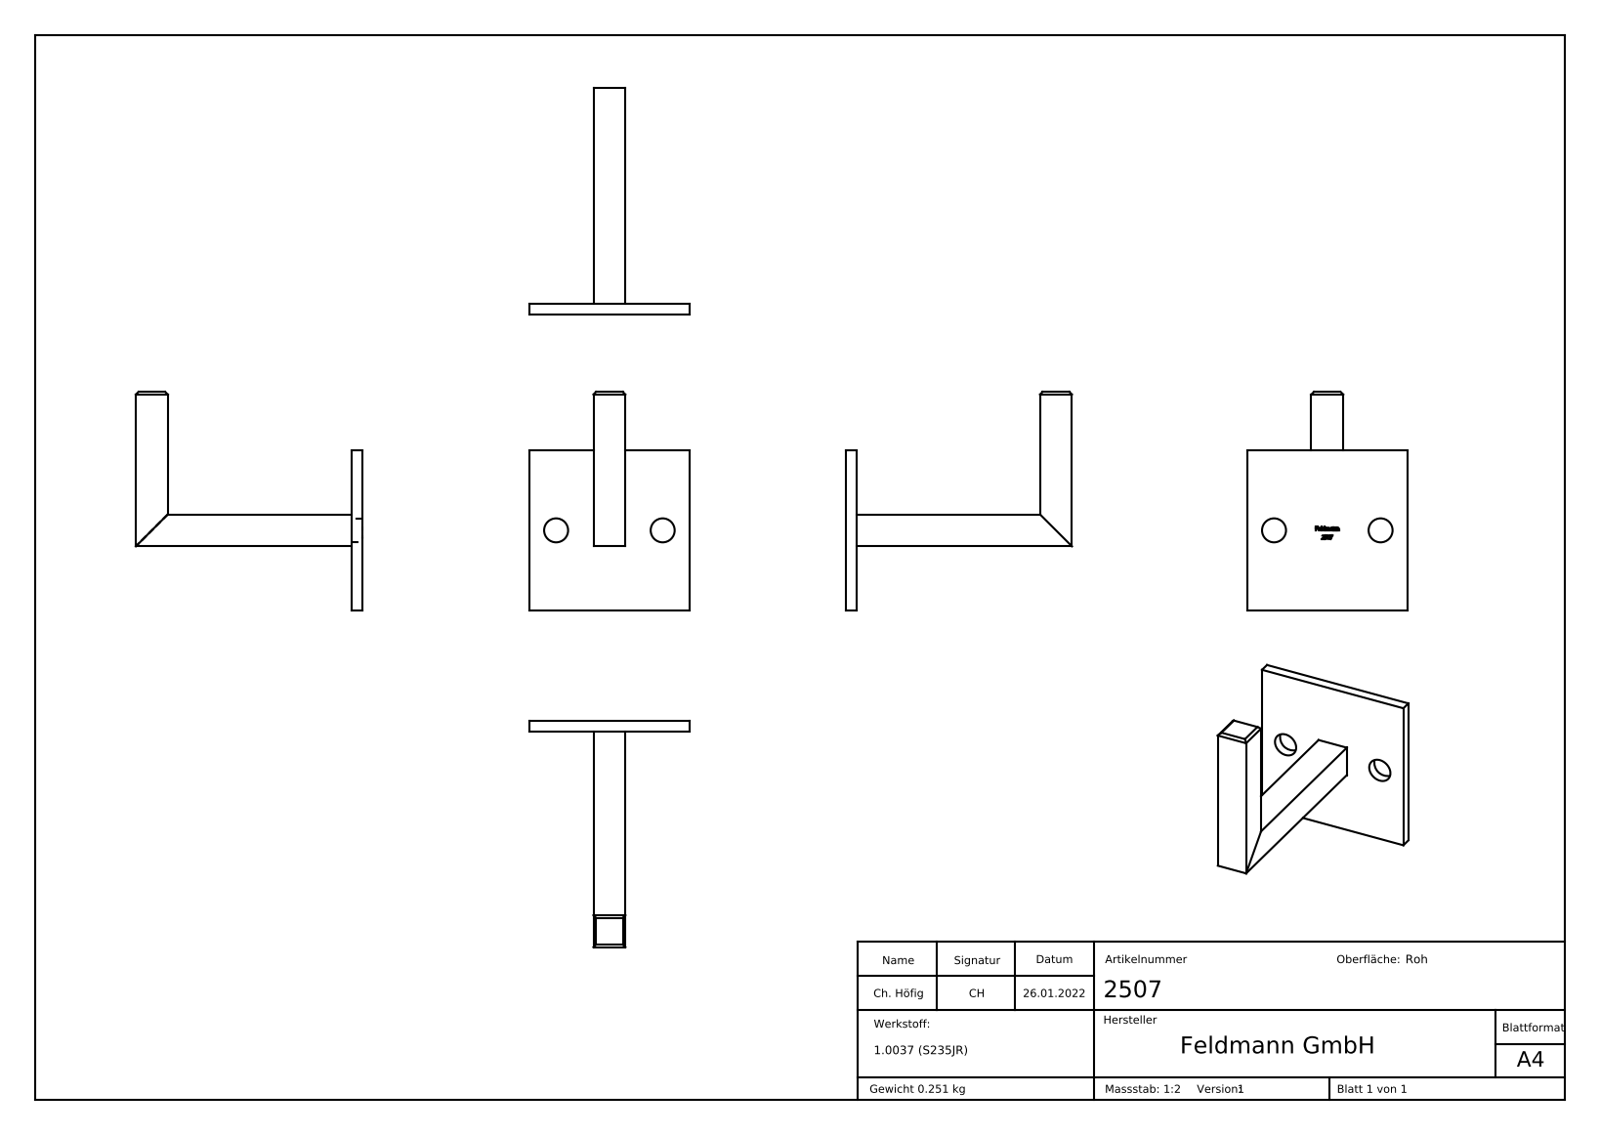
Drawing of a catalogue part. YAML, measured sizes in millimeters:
part_name: "2507"
step_written_by: "SolidWorks 2018 (CONFIG_CONTROL_DESIGN)"
units: millimeters
bodies: {solids: 1, faces: 182, planar: 107, cylindrical: 4, other: 71}
overall_size: [85, 82, 60]
volume: 32156
surface_area: 14205
round_holes:
  - {diameter: 9, count: 2}
face_to_face_distances: [4, 12, 24, 36, 85, 81, 73, 69, 60, 82]
hole_center_spacings: [40]
